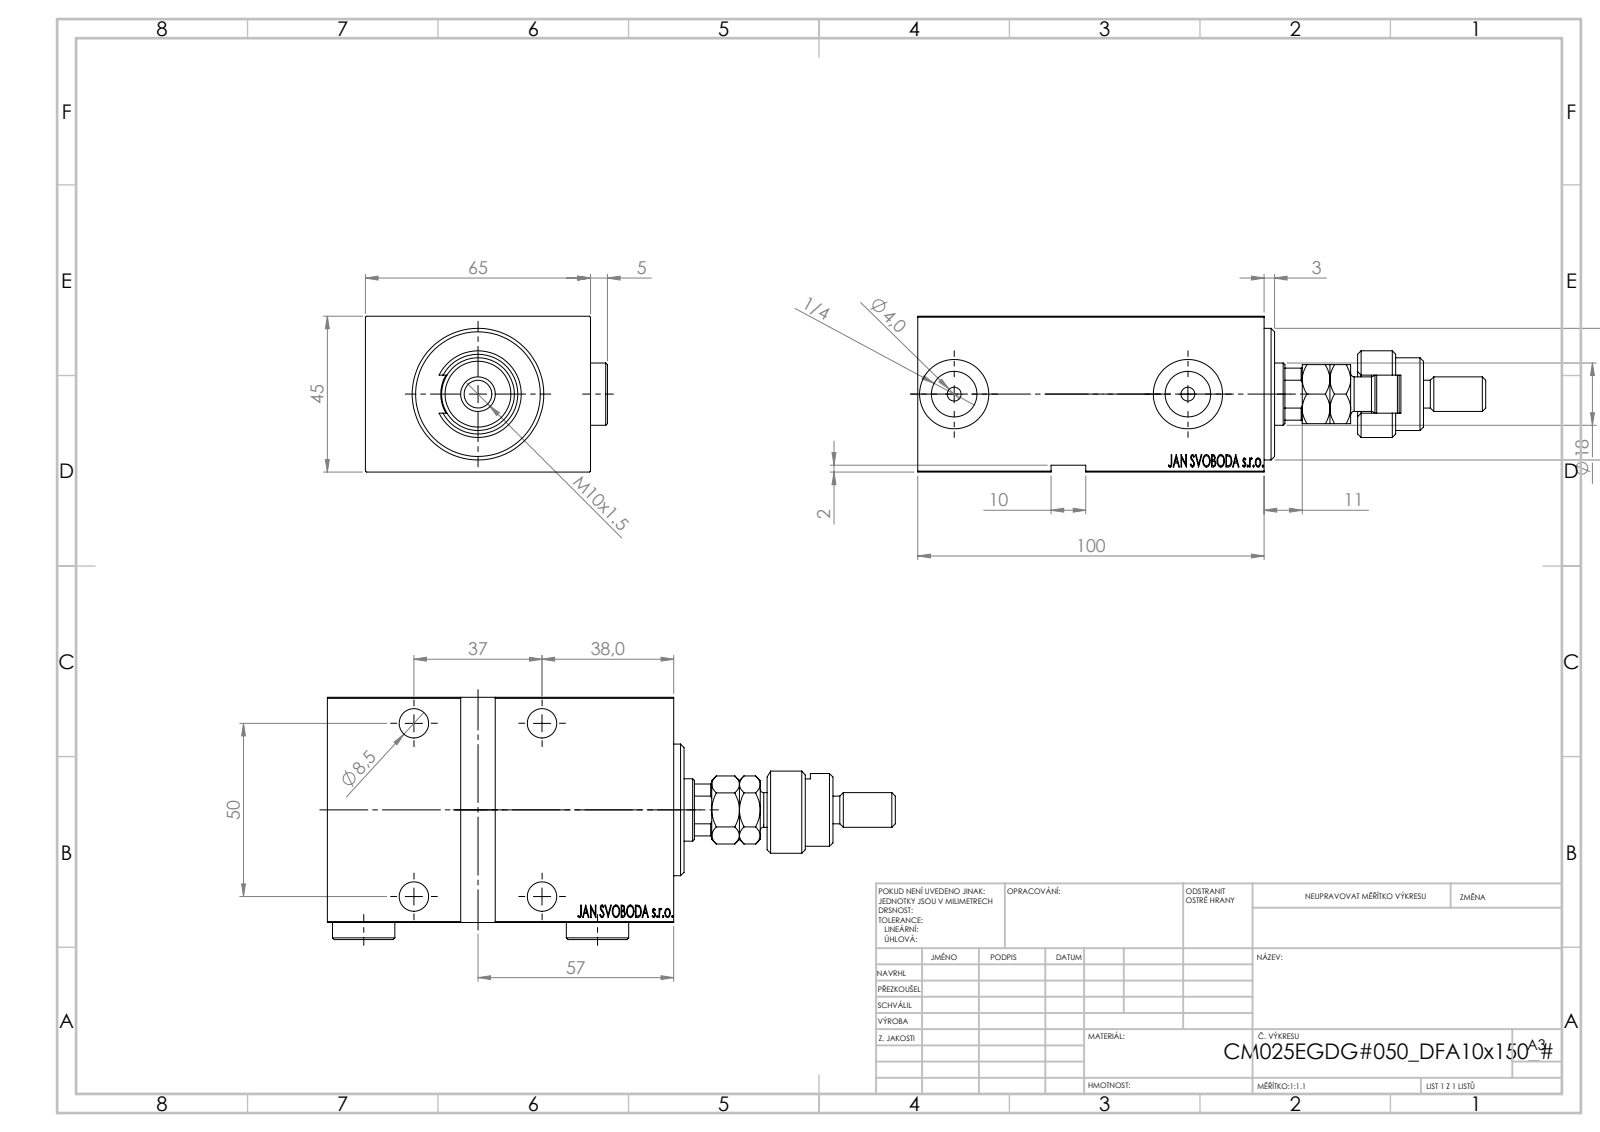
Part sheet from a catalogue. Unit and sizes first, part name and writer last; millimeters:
Units: millimetres
Overall size (bounding box): 164 × 69.9 × 45
Round holes (diameter × count): ⌀8.5 ×5, ⌀13.5 ×4, ⌀4 ×2, ⌀13.16 ×2, ⌀20 ×2, ⌀18 ×1, ⌀21.5 ×1, ⌀35 ×1
Round bosses / shafts (diameter × count): ⌀18 ×2, ⌀38 ×1, ⌀27 ×1, ⌀25 ×1, ⌀21 ×1, ⌀16 ×1, ⌀10 ×1, ⌀8 ×1
Partial cylindrical surfaces — rounded edges, fillets, slot ends (radius × count): R5.5 ×1, R8.5 ×1, R8.75 ×1
Main face-to-face distances: 45, 65, 100, 5, 64.9, 6, 8, 2, 94, 43
Hole centre spacings: 37, 50, 62.2, 67.5
Volume: 277 834 mm³ · Surface area: 62 979 mm²
Bodies: 7 solids, 995 faces (472 planar, 81 cylindrical, 442 other)
Part name (STEP PRODUCT): MFA; Zatka_OIL_PORT; V450CM_VC_B; FEMALE_PART_FOR_DFA (+2 more)
STEP written by: SolidWorks 2019 (CONFIG_CONTROL_DESIGN)
